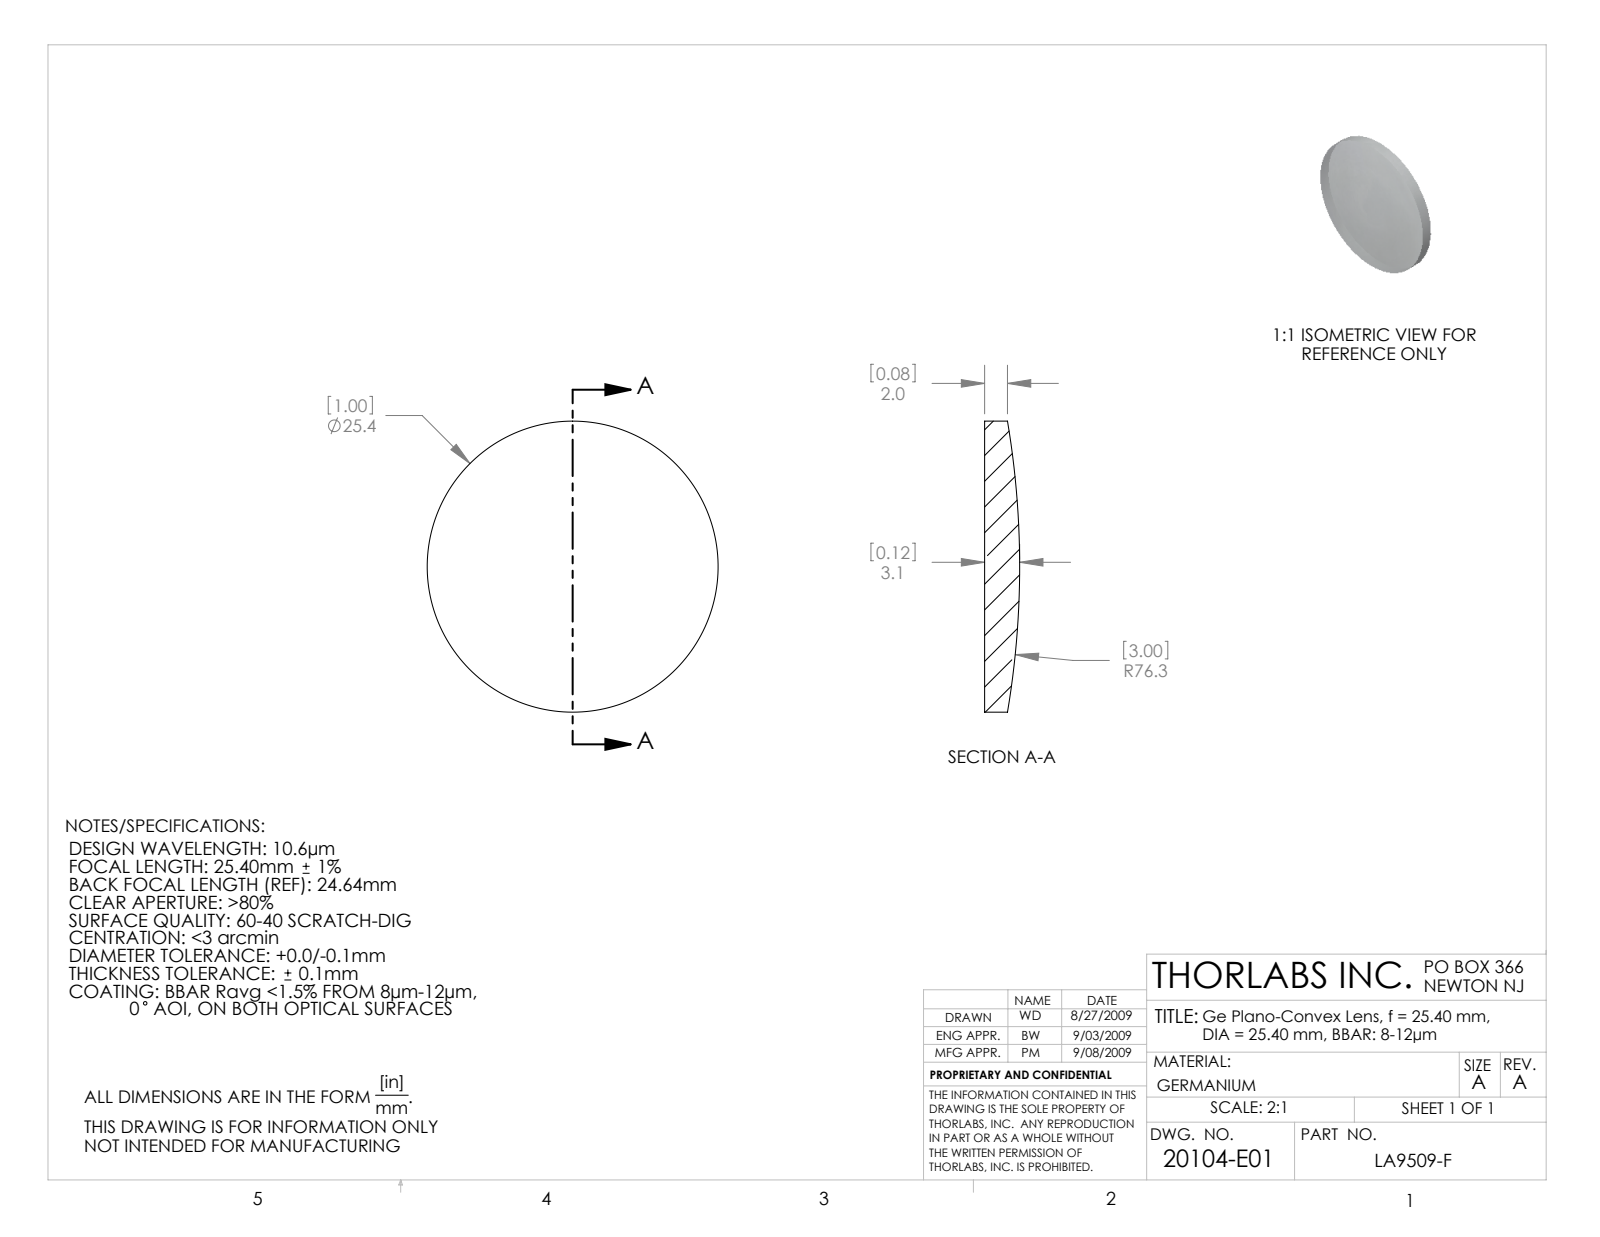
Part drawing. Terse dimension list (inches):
name: 20104-E0W
written by: SolidWorks 2007 (CONFIG_CONTROL_DESIGN)
unit: in
bodies: 1 solid, 5 faces (1 planar, 2 cylindrical, 2 other)
size: 1 × 1 × 0.12
volume: 0.078 in³; area: 1.823 in²
bosses: 1× ⌀1
